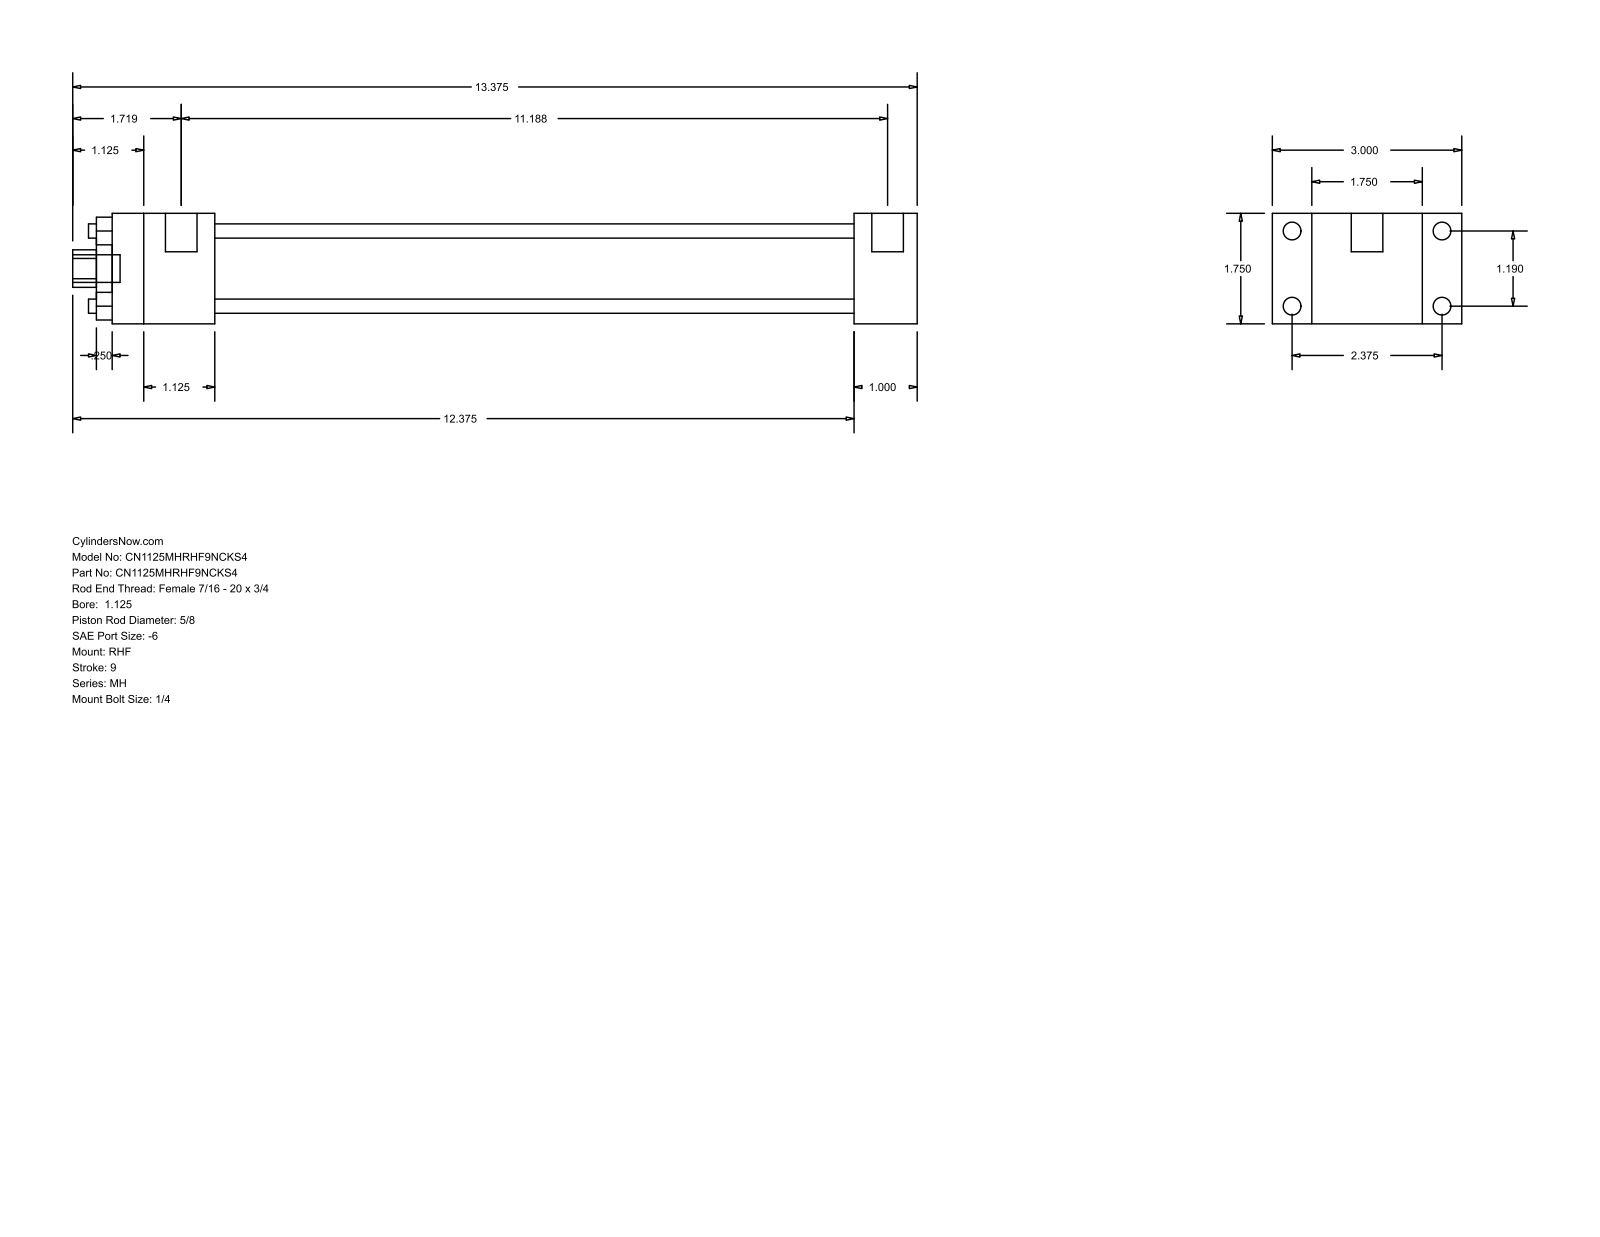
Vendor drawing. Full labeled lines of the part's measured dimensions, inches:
Part name (STEP PRODUCT): MH_RHF__0112_0.625
STEP written by: GSSL Pune (CONFIG_CONTROL_DESIGN)
Units: inches
Bodies: 0 solids, 88 faces (60 planar, 28 cylindrical, 0 other)
Overall size (bounding box): 13.375 × 3 × 1.75
Round holes (diameter × count): ⌀0.225 ×4, ⌀0.625 ×1, ⌀1.125 ×1, ⌀1.375 ×1
Round bosses / shafts (diameter × count): ⌀0.281 ×4, ⌀0.219 ×4, ⌀0.5 ×2, ⌀0.437 ×1
Partial cylindrical surfaces — rounded edges, fillets, slot ends (radius × count): R0.297 ×1
Main face-to-face distances: 1.75, 0.625, 2.375, 1, 3, 10.125, 11.125, 1.625, 11.75, 12.75
Hole centre spacings: 0.841, 1.19, 1.683
